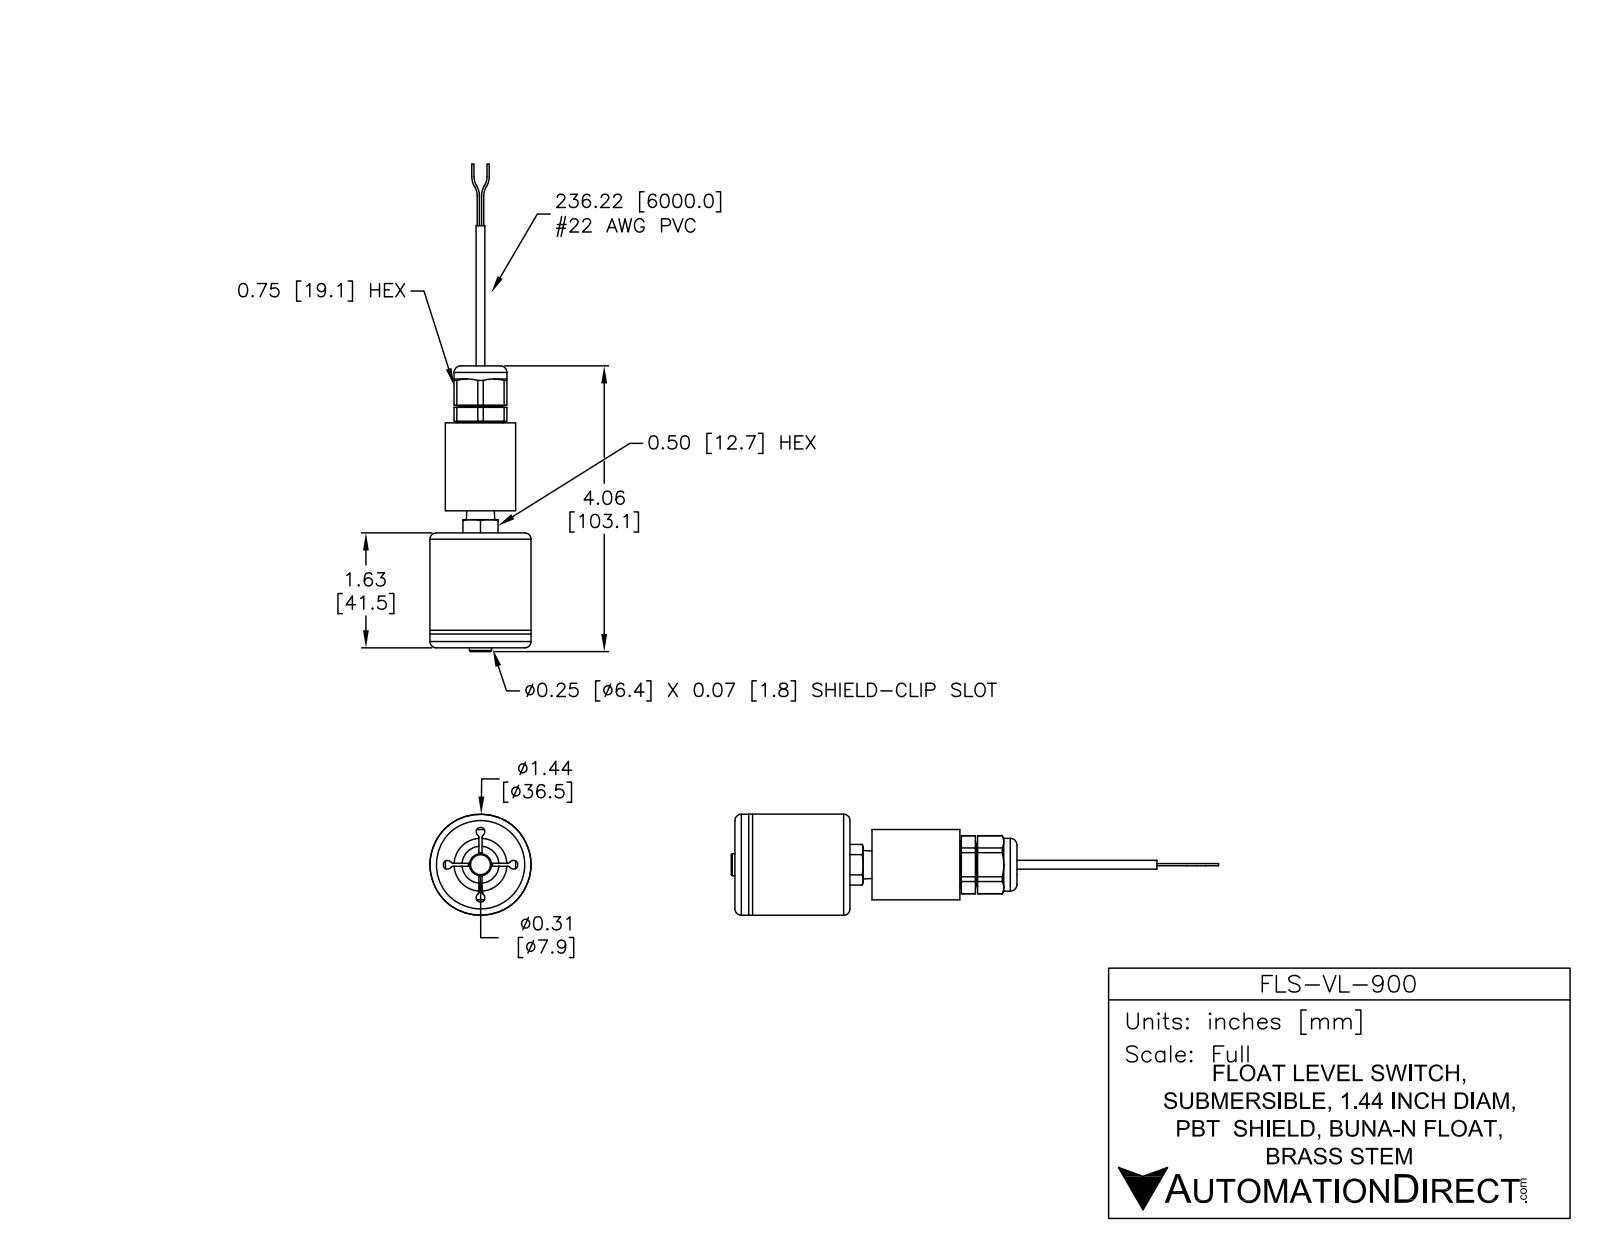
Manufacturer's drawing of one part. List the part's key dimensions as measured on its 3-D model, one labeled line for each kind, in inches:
Part name (STEP PRODUCT): FLS-VL-900
STEP written by: SolidWorks 2013 (AUTOMOTIVE_DESIGN)
Units: inches
Bodies: 3 solids, 202 faces (81 planar, 85 cylindrical, 36 other)
Overall size (bounding box): 5.984 × 1.437 × 1.437
Volume: 1.784 in³ · Surface area: 35.4 in²
Round holes (diameter × count): ⌀0.125 ×4, ⌀0.5 ×2, ⌀0.21 ×1, ⌀0.344 ×1, ⌀0.594 ×1, ⌀1.312 ×1, ⌀1.393 ×1
Round bosses / shafts (diameter × count): ⌀0.04 ×4, ⌀0.02 ×2, ⌀1.437 ×1, ⌀1 ×1, ⌀0.873 ×1, ⌀0.73 ×1, ⌀0.594 ×1, ⌀0.313 ×1
Partial cylindrical surfaces — rounded edges, fillets, slot ends (radius × count): R0.1 ×12, R0.164 ×2
Main face-to-face distances: 1.508, 3.228, 1.477, 1.868, 0.391, 0.031, 0.36, 0.11, 1.587, 1.618
Hole centre spacings: 0.5, 0.707, 1, 0.5, 0.5
